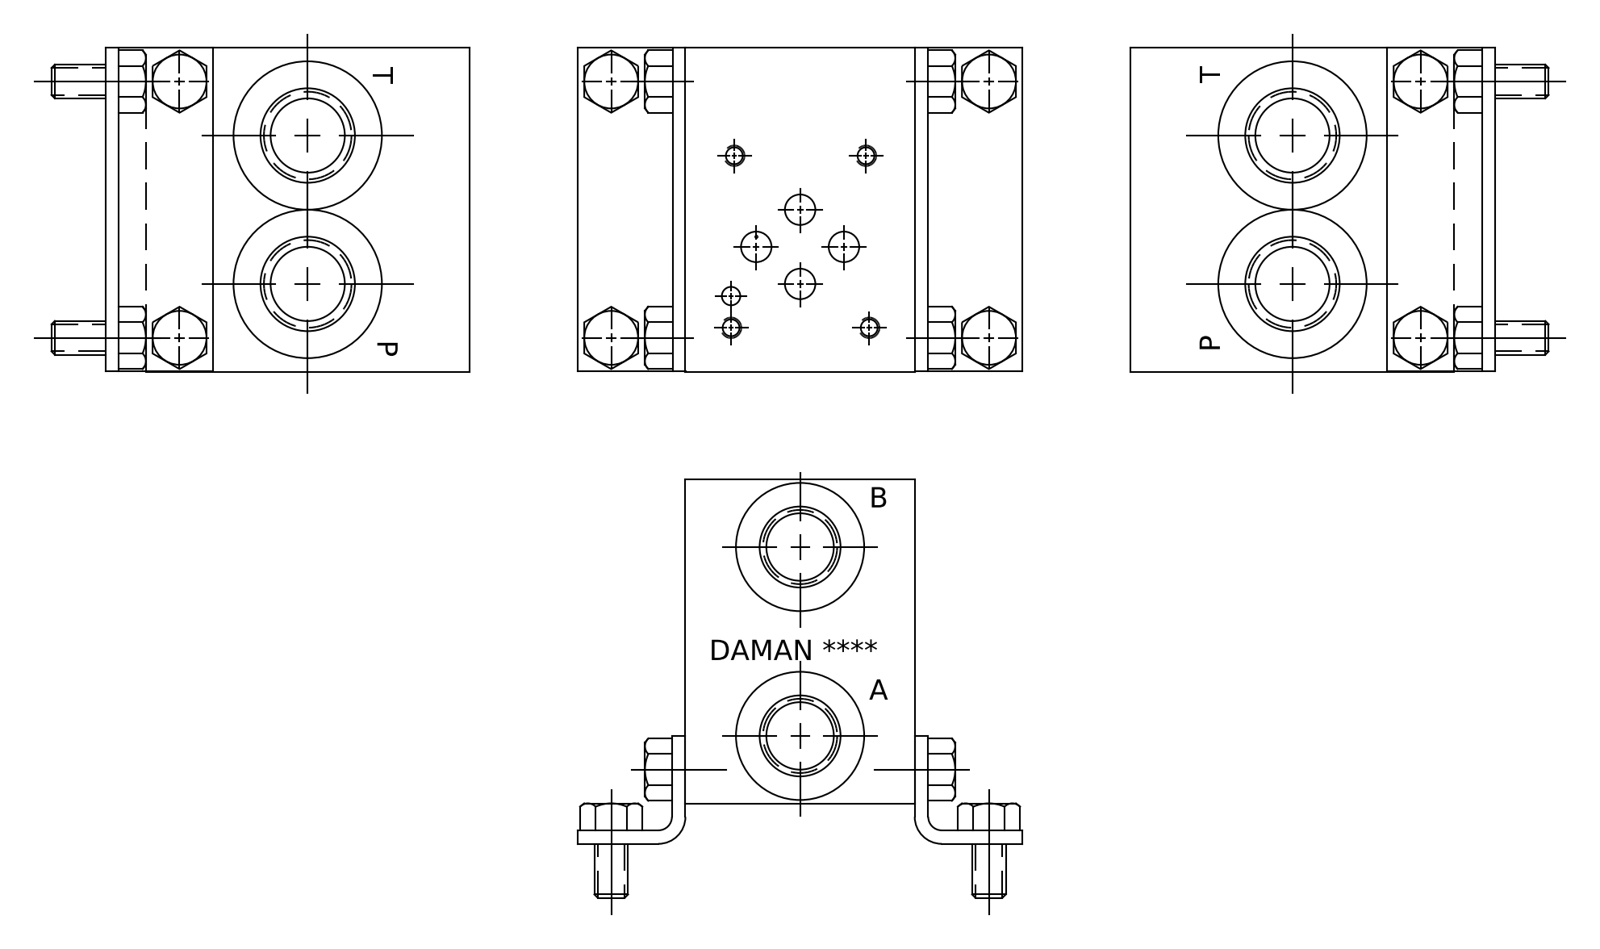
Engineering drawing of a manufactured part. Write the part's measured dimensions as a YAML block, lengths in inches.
part_name: "Part_SD03P012S_3D"
step_written_by: "Autodesk Inventor 2019 (AUTOMOTIVE_DESIGN)"
units: inches
bodies: {solids: 1, faces: 518, planar: 298, cylindrical: 55, other: 165}
overall_size: [3, 3, 2.125]
volume: 15.76
surface_area: 62.16
round_holes:
  - {diameter: 0.149, count: 4}
  - {diameter: 0.19, count: 4}
  - {diameter: 0.281, count: 3}
  - {diameter: 0.257, count: 2}
  - {diameter: 0.312, count: 2}
  - {diameter: 0.625, count: 2}
  - {diameter: 0.688, count: 2}
  - {diameter: 0.689, count: 2}
  - {diameter: 0.75, count: 2}
  - {diameter: 0.758, count: 2}
  - {diameter: 0.805, count: 2}
  - {diameter: 0.875, count: 2}
face_to_face_distances: [3, 2.125, 0.031, 2.094, 2.063, 2.969, 0.687, 1.438, 0.656, 1.407]
hole_center_spacings: [0.785, 0.868, 1.283, 1.321, 1.594, 2.026, 2.233, 0.295]
